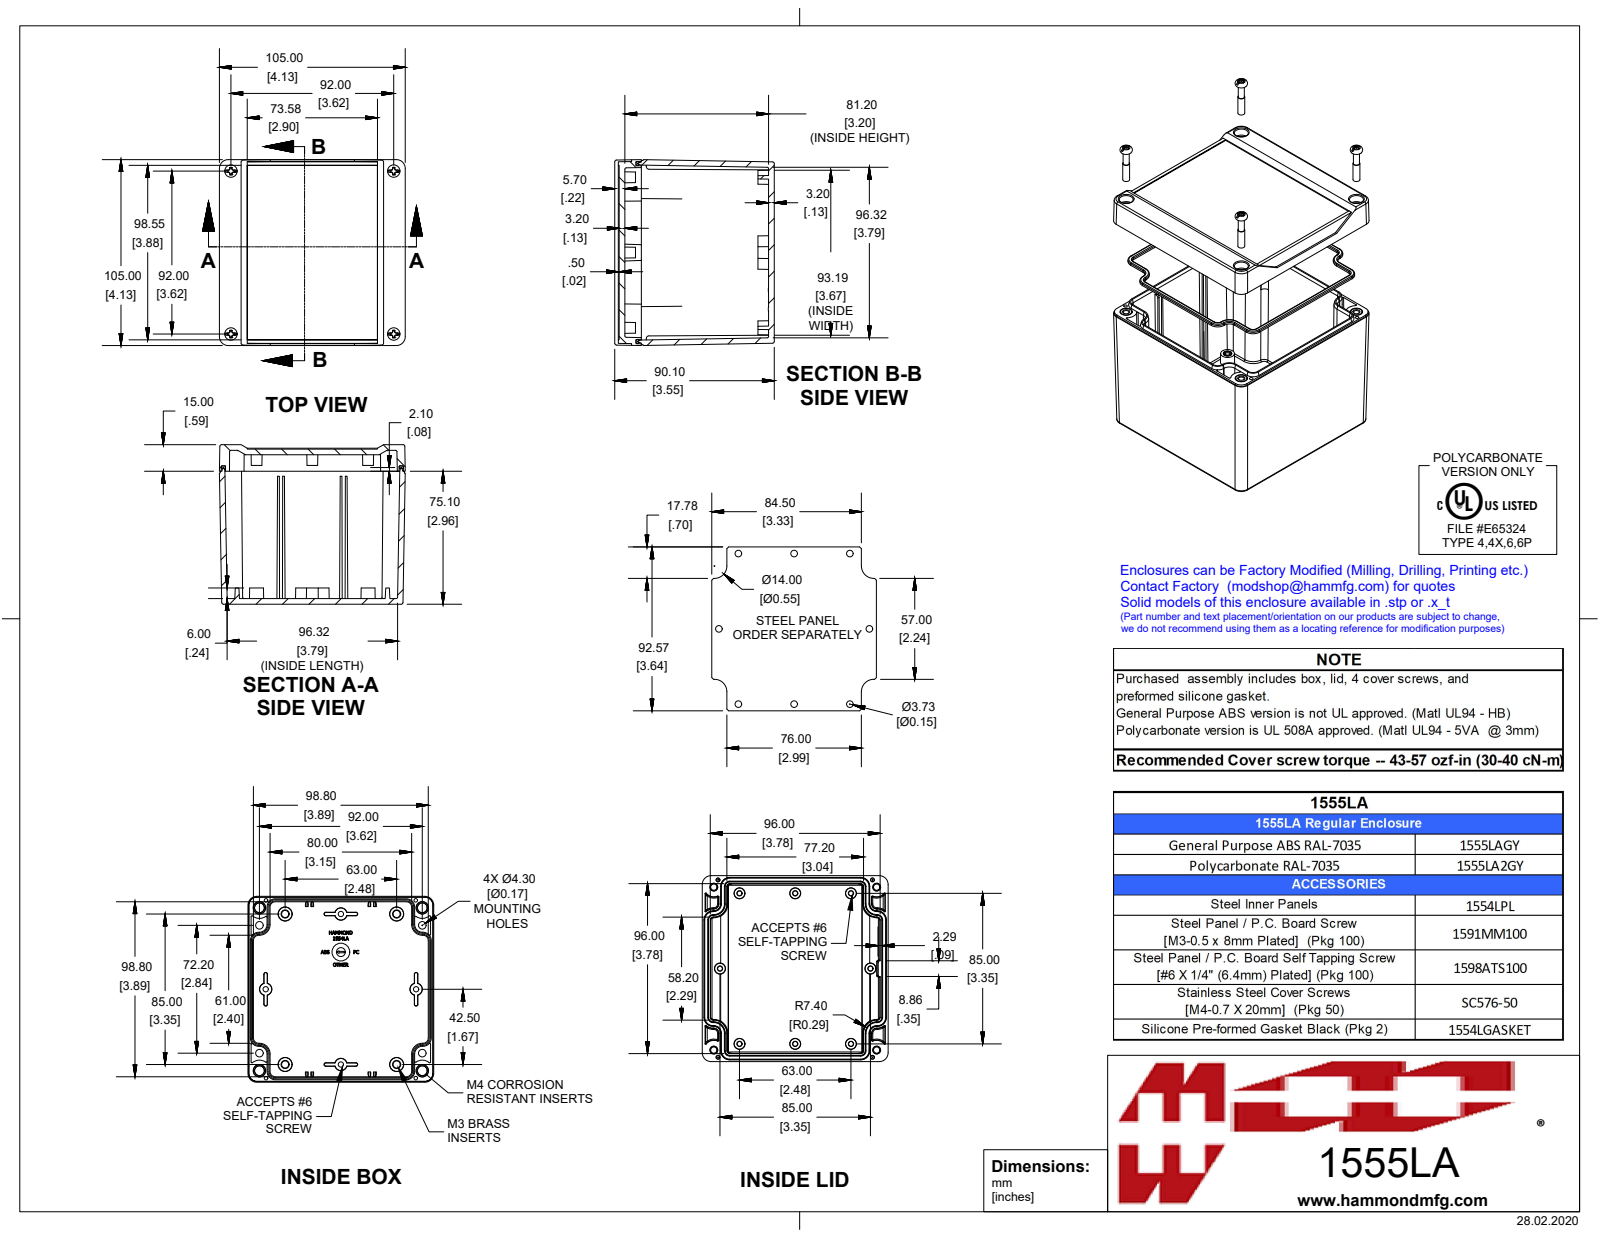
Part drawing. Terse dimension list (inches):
name: 1555LA2GY
written by: SolidWorks 2019 (AUTOMOTIVE_DESIGN)
unit: in
bodies: 15 solids, 1928 faces (657 planar, 381 cylindrical, 890 other)
size: 4.134 × 4.134 × 3.547
volume: 12.46 in³; area: 220.2 in²
holes: 4× ⌀0.097, 4× ⌀0.128, 4× ⌀0.181, 3× ⌀0.138
bosses: 4× ⌀0.25, 4× ⌀0.218, 4× ⌀0.21, 4× ⌀0.19, 4× ⌀0.154, 4× ⌀0.153, 4× ⌀0.15, 4× ⌀0.135
rounds: 26× R0.02, 22× R0.012, 12× R0.039, 10× R0.031, 8× R0.104, 8× R0.197, 8× R0.199, 4× R0.118
face distances: 0.122, 0.126, 3.323, 3.449, 3.197, 4.134, 4.012, 0.098, 0.071, 3.957
hole spacings: 0.587, 3.054, 3.531, 3.622, 4.631, 2.48, 3.346, 4.165
